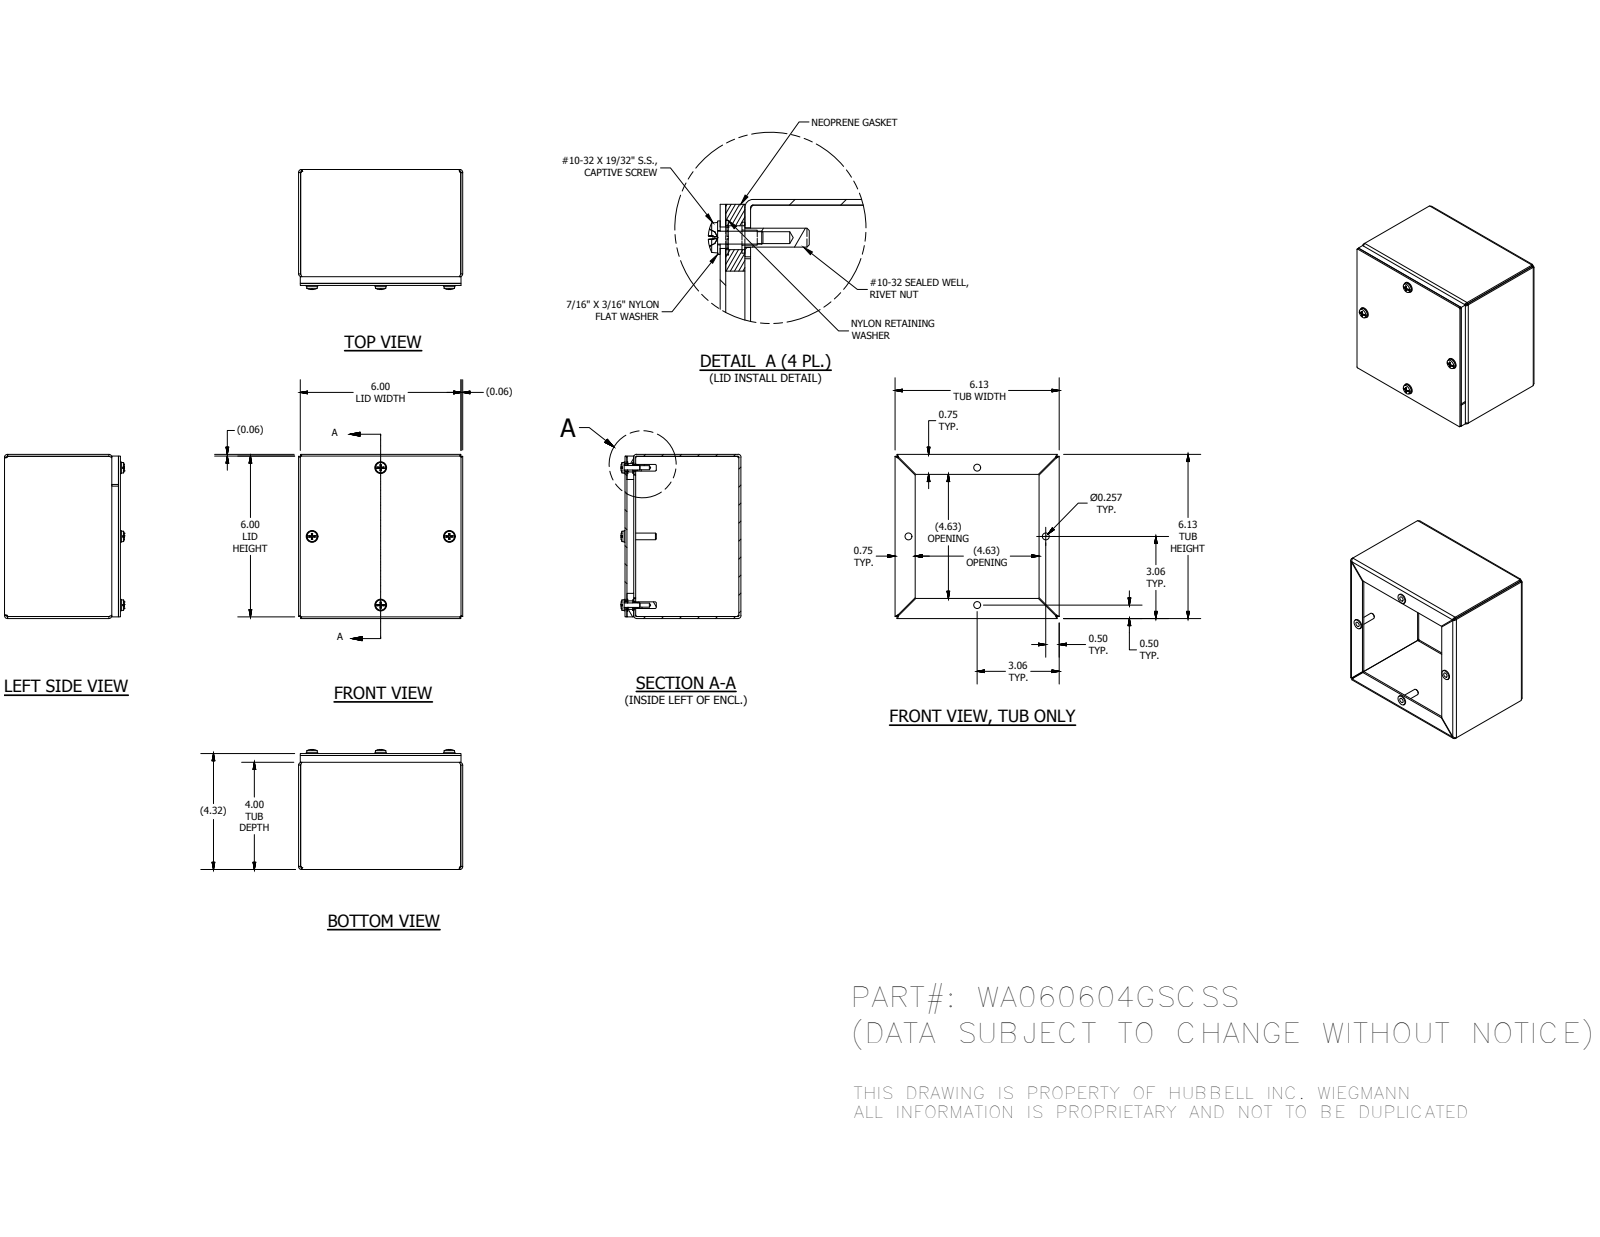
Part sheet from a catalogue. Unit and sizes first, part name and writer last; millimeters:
Units: millimetres
Overall size (bounding box): 155.57 × 155.57 × 113.75
Round holes (diameter × count): ⌀3.96 ×4, ⌀4.78 ×4, ⌀4.98 ×4, ⌀6.53 ×4, ⌀7.06 ×4, ⌀7.14 ×4, ⌀7.95 ×4
Round bosses / shafts (diameter × count): ⌀11.51 ×4, ⌀11.11 ×4, ⌀10.31 ×4, ⌀6.3 ×4, ⌀4.25 ×4
Partial cylindrical surfaces — rounded edges, fillets, slot ends (radius × count): R0.79 ×12, R1.78 ×8, R2.67 ×8, R2.27 ×4
Main face-to-face distances: 1.88, 153.7, 107.95, 151.82, 155.58, 99.72, 8.23, 106.07, 109.83, 6.35
Hole centre spacings: 92.04, 92.02, 92.05, 130.16, 130.14, 130.18
Volume: 294 559 mm³ · Surface area: 273 725 mm²
Bodies: 20 solids, 440 faces (244 planar, 96 cylindrical, 100 other)
Part name (STEP PRODUCT): WA060604GSCSSBKP; WA0606GSCSSLID; 316279; 37210 (+4 more)
STEP written by: Autodesk Inventor 2016 (AUTOMOTIVE_DESIGN)
